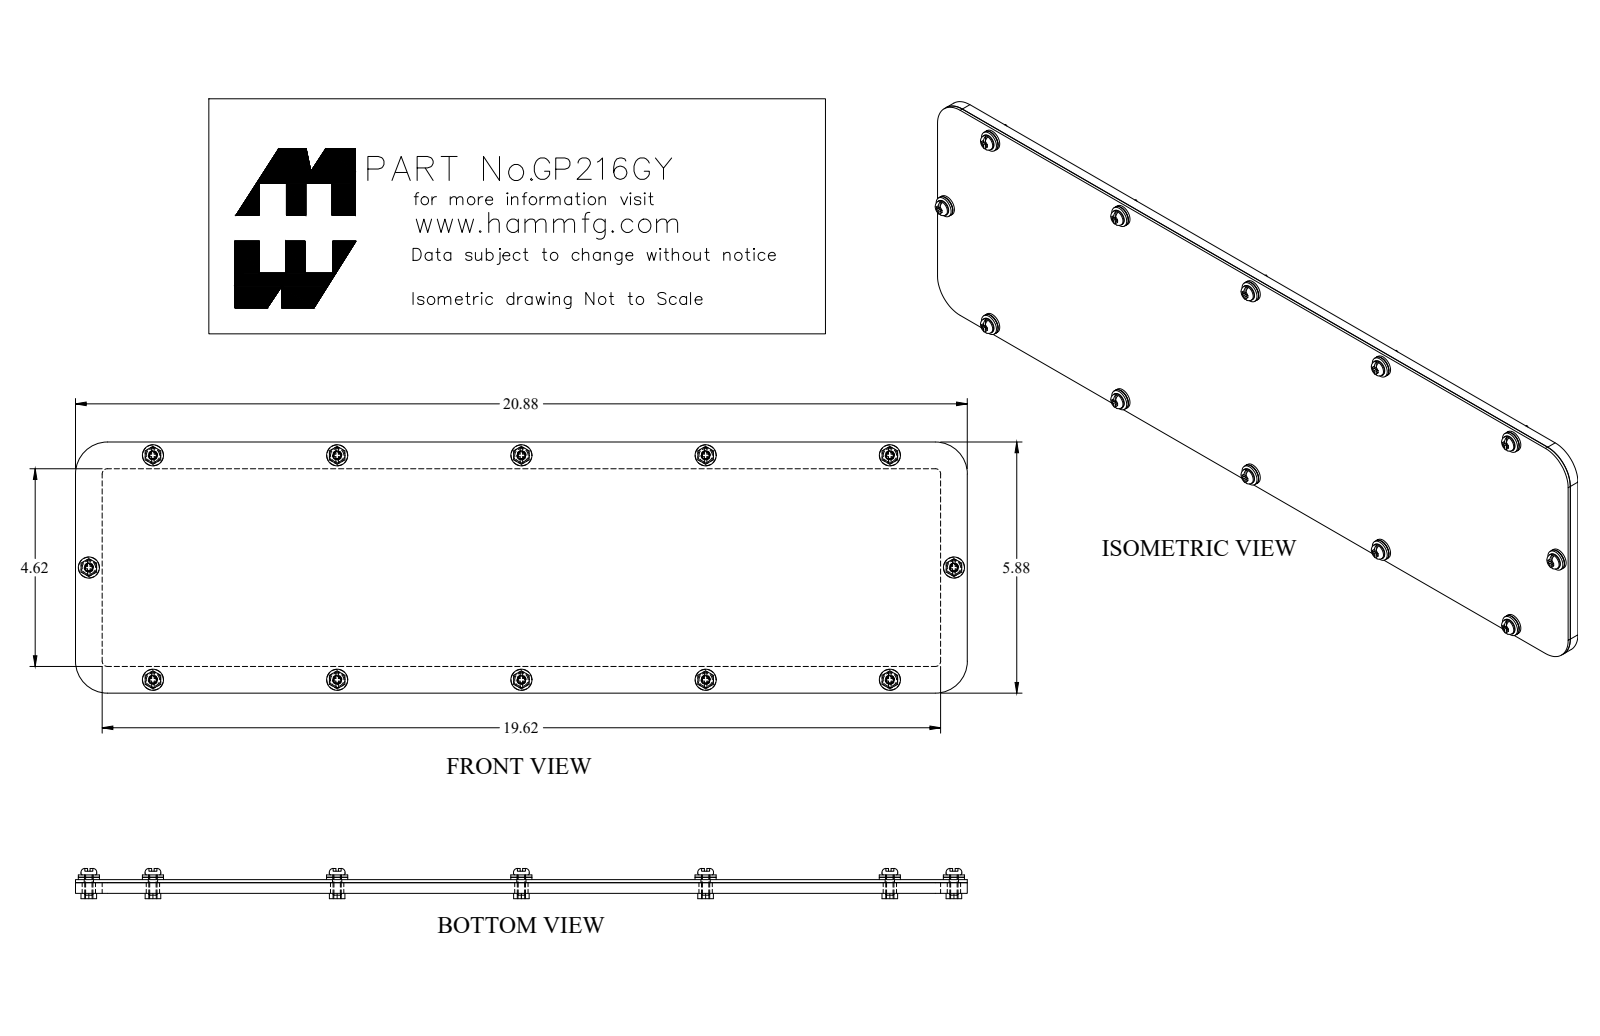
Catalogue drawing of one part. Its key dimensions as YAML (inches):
part_name: "GP216GY"
step_written_by: "SolidWorks 2018 (AUTOMOTIVE_DESIGN)"
units: inches
bodies: {solids: 38, faces: 664, planar: 364, cylindrical: 228, other: 72}
overall_size: [20.875, 5.875, 0.707]
volume: 17.05
surface_area: 356.4
round_holes:
  - {diameter: 0.156, count: 12}
  - {diameter: 0.197, count: 12}
  - {diameter: 0.218, count: 12}
  - {diameter: 0.313, count: 12}
round_bosses_or_shafts:
  - {diameter: 0.494, count: 12}
  - {diameter: 0.488, count: 12}
  - {diameter: 0.367, count: 12}
  - {diameter: 0.19, count: 12}
partial_cylinders:
  - {radius: 0.125, count: 4}
  - {radius: 0.75, count: 4}
face_to_face_distances: [0.072, 0.322, 0.25, 0.625, 5.25, 5.875, 4.625, 0.11, 0.182, 0.432]
hole_center_spacings: [4.312, 8.624, 6.794, 12.937, 10.097, 6.794, 10.097, 13.962]
